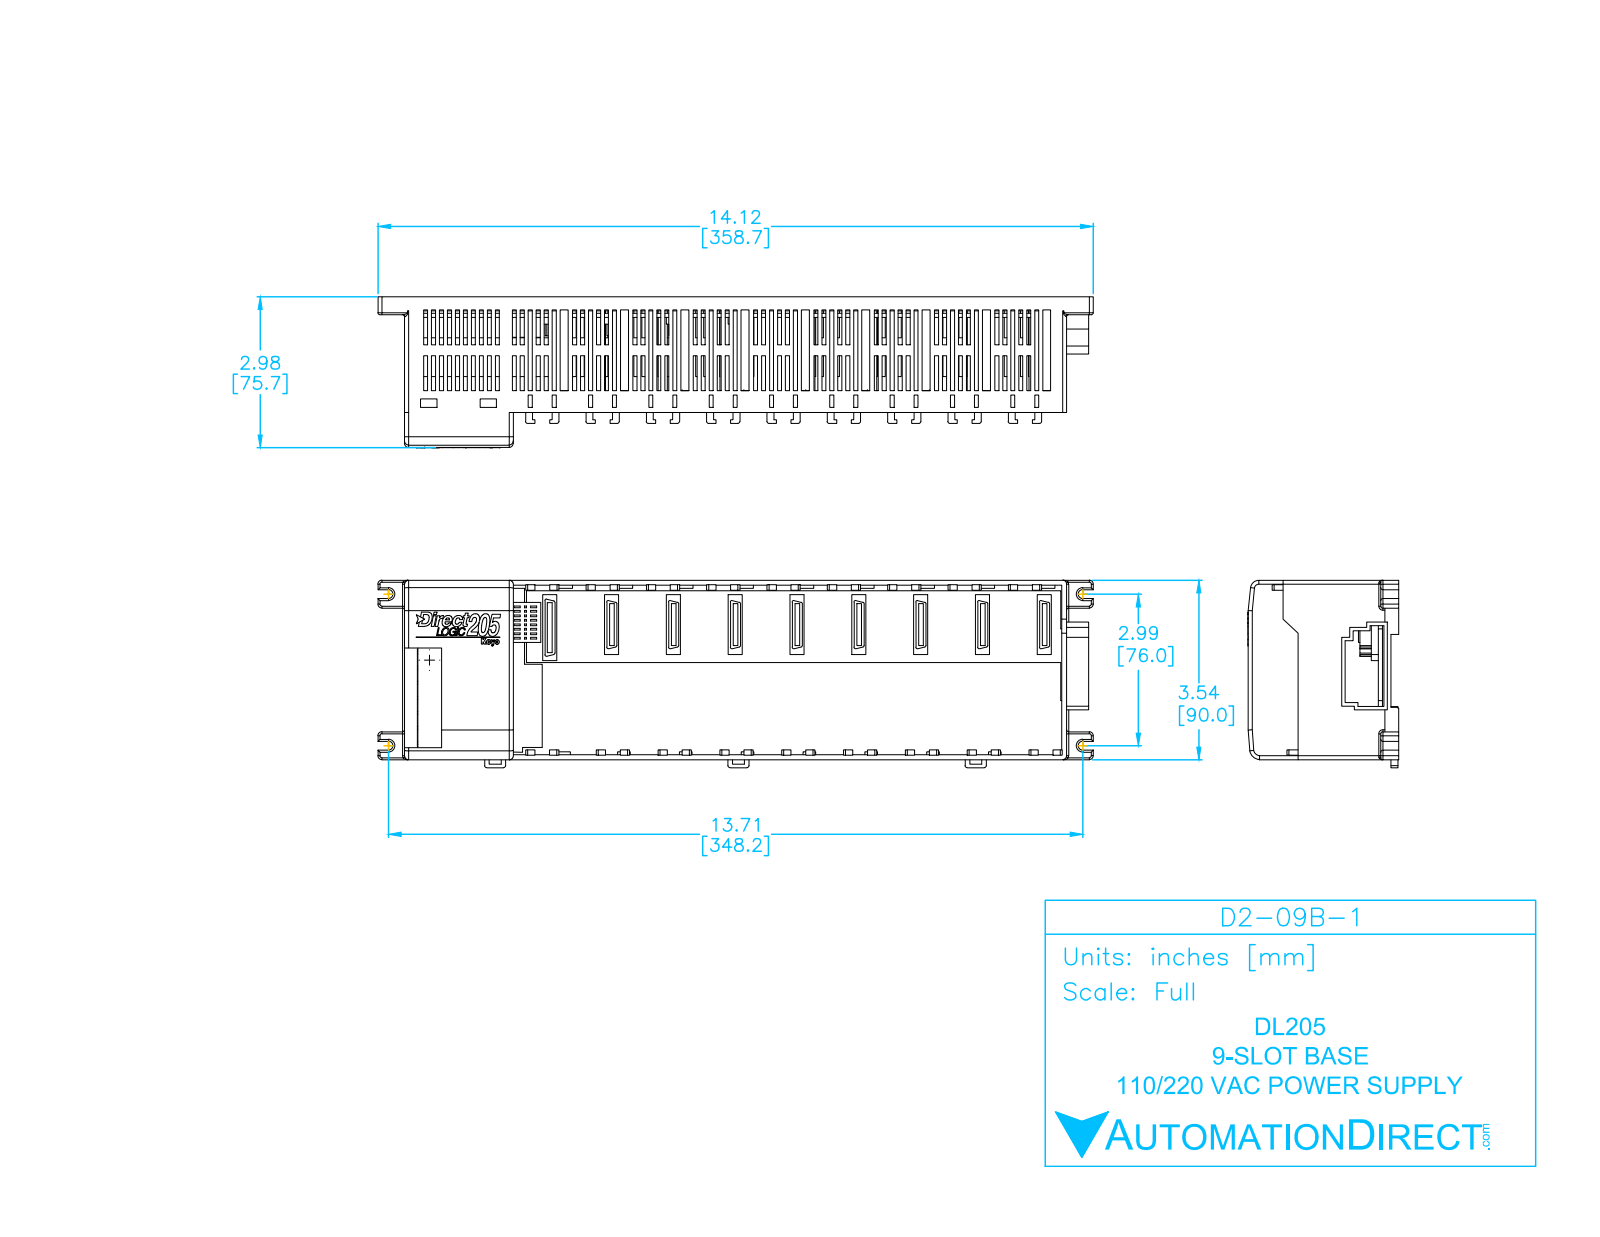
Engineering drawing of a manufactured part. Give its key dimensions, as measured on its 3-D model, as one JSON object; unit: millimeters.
{"part_name": "D2-09B-1", "step_written_by": "SolidWorks 2009 (AUTOMOTIVE_DESIGN)", "units": "millimeters", "bodies": {"solids": 7, "faces": 3025, "planar": 2640, "cylindrical": 219, "other": 166}, "overall_size": [358.68, 94, 75.7], "volume_mm3": 354279, "surface_area_mm2": 251686, "round_bosses_or_shafts": [[5.42, 6]], "partial_cylinders_radius": [[1, 86], [0.75, 36], [0.25, 24], [2, 20], [2.21, 4], [4.71, 4], [4.12, 1], [5.29, 1]], "face_to_face_distances": [2.5, 3, 85, 1.25, 87.5, 2, 4.25, 6.25, 3.25, 90]}
